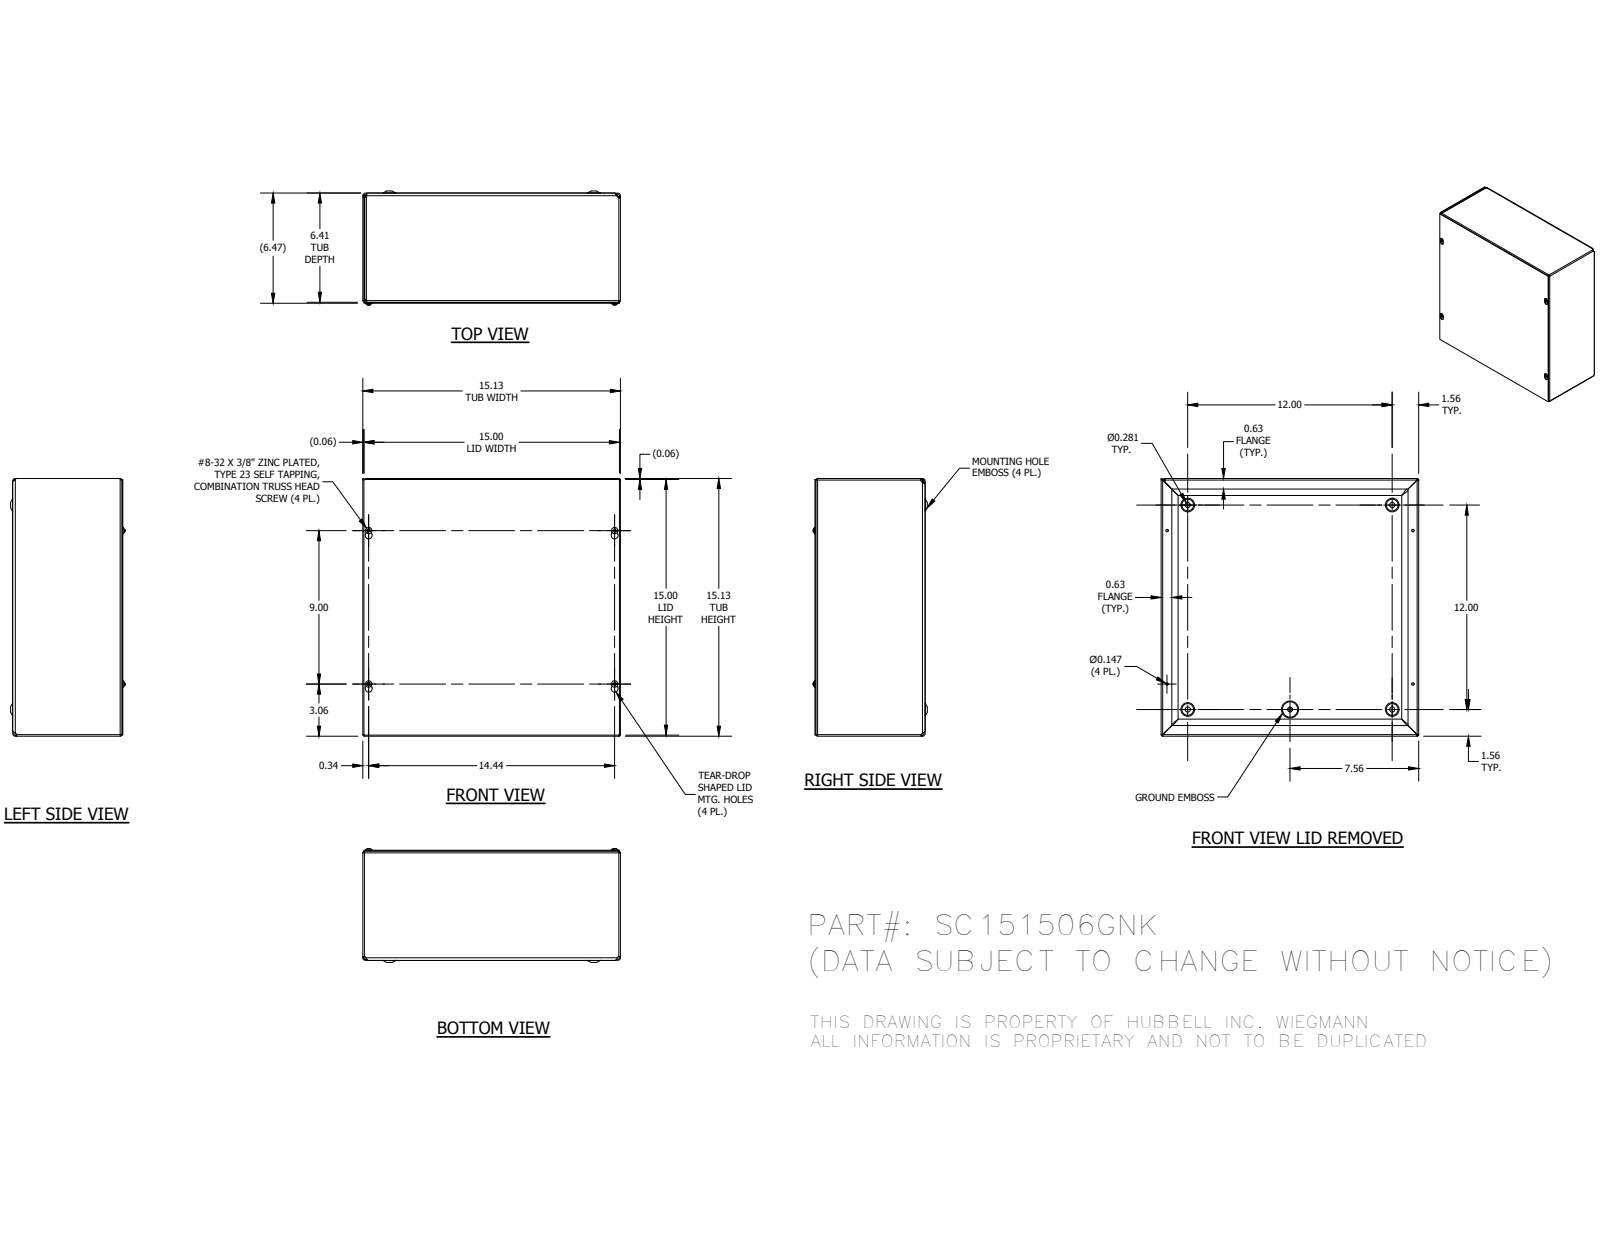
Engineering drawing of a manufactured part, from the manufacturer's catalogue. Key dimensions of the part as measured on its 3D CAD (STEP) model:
Part name (STEP PRODUCT): SC1515GNKBKP; SC151506GNKWRA; SC1515GNKLID; 34056 (+1 more)
STEP written by: Autodesk Inventor 2014 (AUTOMOTIVE_DESIGN)
Units: millimetres
Bodies: 7 solids, 358 faces (133 planar, 73 cylindrical, 152 other)
Overall size (bounding box): 384.18 × 384.18 × 170
Volume: 925 124 mm³ · Surface area: 1 184 000 mm²
Round holes (diameter × count): ⌀3.73 ×4, ⌀7.62 ×4, ⌀4.19 ×1
Round bosses / shafts (diameter × count): ⌀9.75 ×4, ⌀4.17 ×4, ⌀5.8 ×1
Partial cylindrical surfaces — rounded edges, fillets, slot ends (radius × count): R0.79 ×8, R2.37 ×8, R1.4 ×4, R1.57 ×4, R2.38 ×4, R2.97 ×4, R3.15 ×4, R3.17 ×4
Main face-to-face distances: 1.57, 161.12, 162.69, 1.58, 1.59, 162.71, 164.28, 382.6, 381.03, 384.18
Hole centre spacings: 304.8, 152.4, 228.6, 268.47, 268.51, 323.63, 337.91, 340.78
